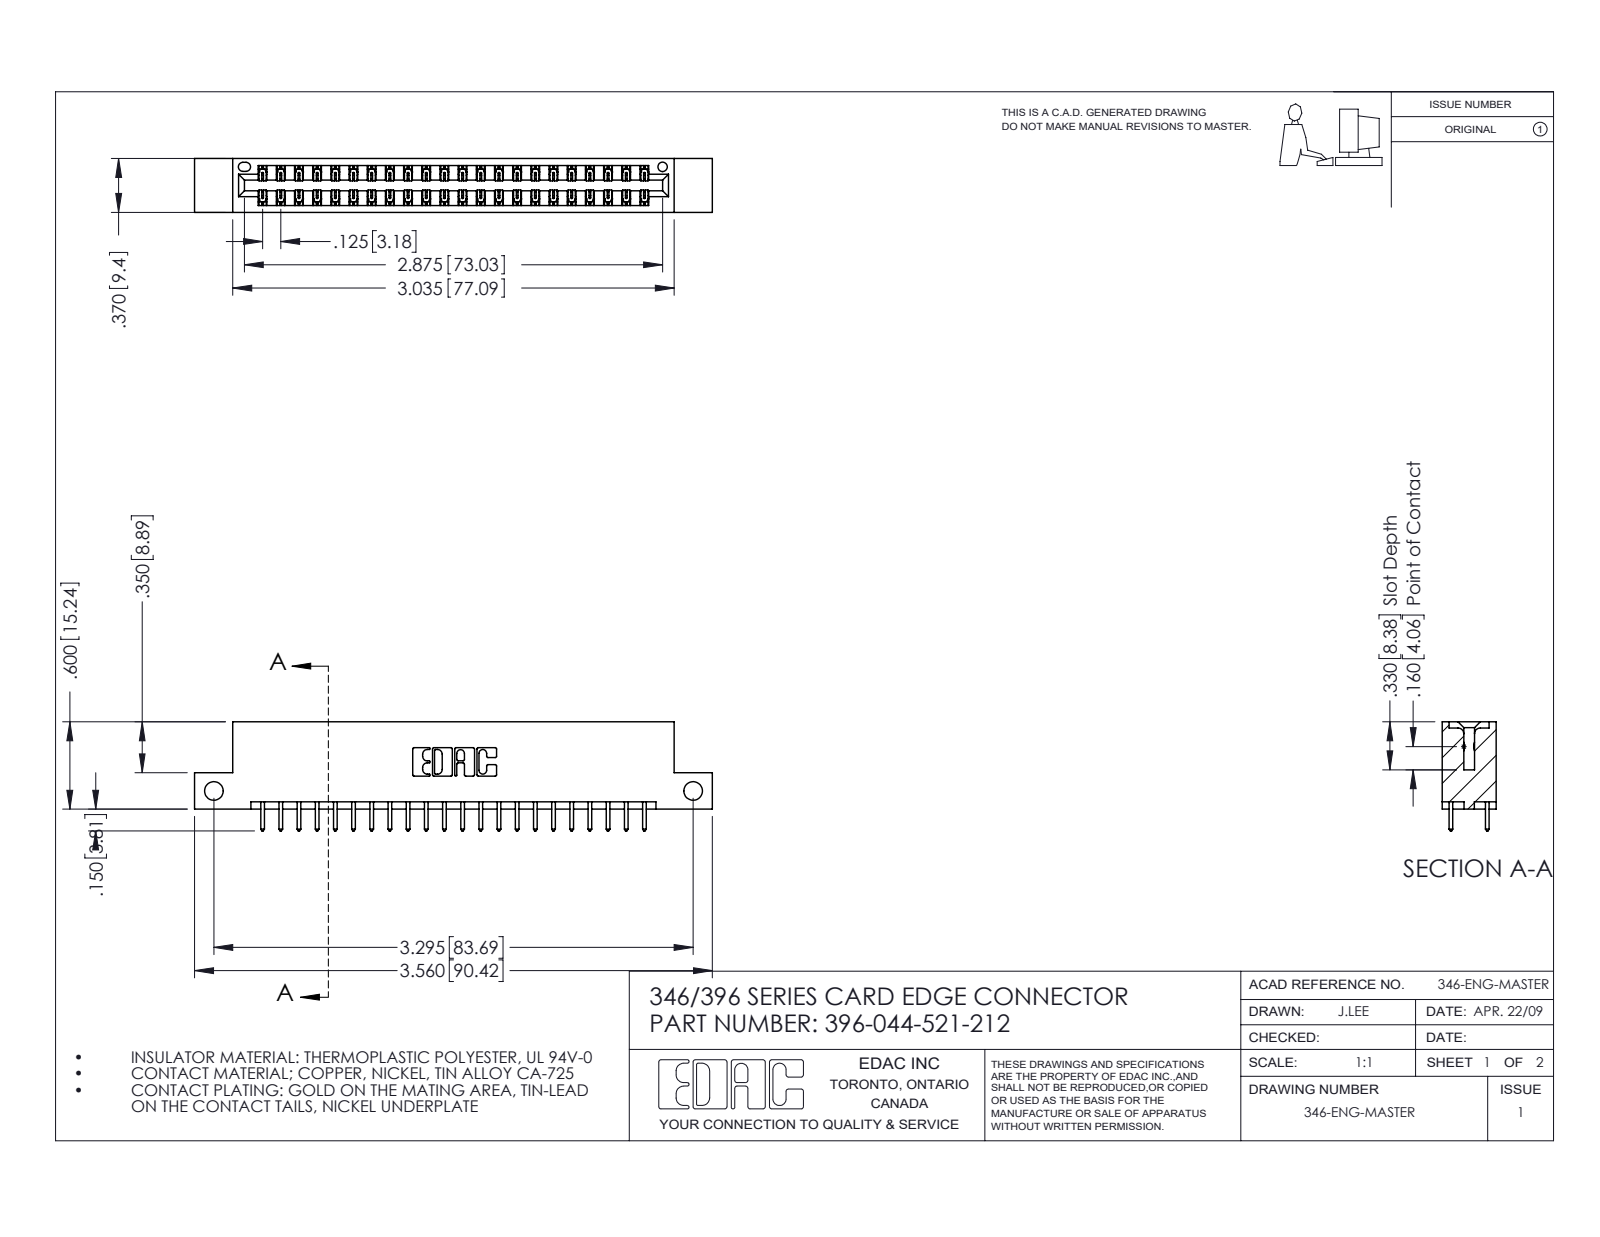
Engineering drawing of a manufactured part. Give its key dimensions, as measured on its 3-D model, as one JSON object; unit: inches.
{"part_name": "345-292-001_345-293-121; 396-044-521-212; 346 Part_Flush Mounting Lugs - Side Mount", "step_written_by": "SolidWorks 2016 (CONFIG_CONTROL_DESIGN)", "units": "inches", "bodies": {"solids": 45, "faces": 2410, "planar": 1616, "cylindrical": 794, "other": 0}, "overall_size": [3.56, 0.75, 0.37], "volume_in3": 0.522, "surface_area_in2": 17.34, "round_holes": [[0.128, 2], [0.064, 1]], "partial_cylinders_radius": [[0.006, 66], [0.01, 44], [0.01, 22], [0.007, 6], [0.031, 6], [0.026, 3], [0.014, 2], [0.022, 2]], "face_to_face_distances": [0.048, 0.322, 0.25, 0.37, 0.072, 0.298, 0.025, 0.275, 0.148, 0.222], "hole_center_spacings": [3.295]}
